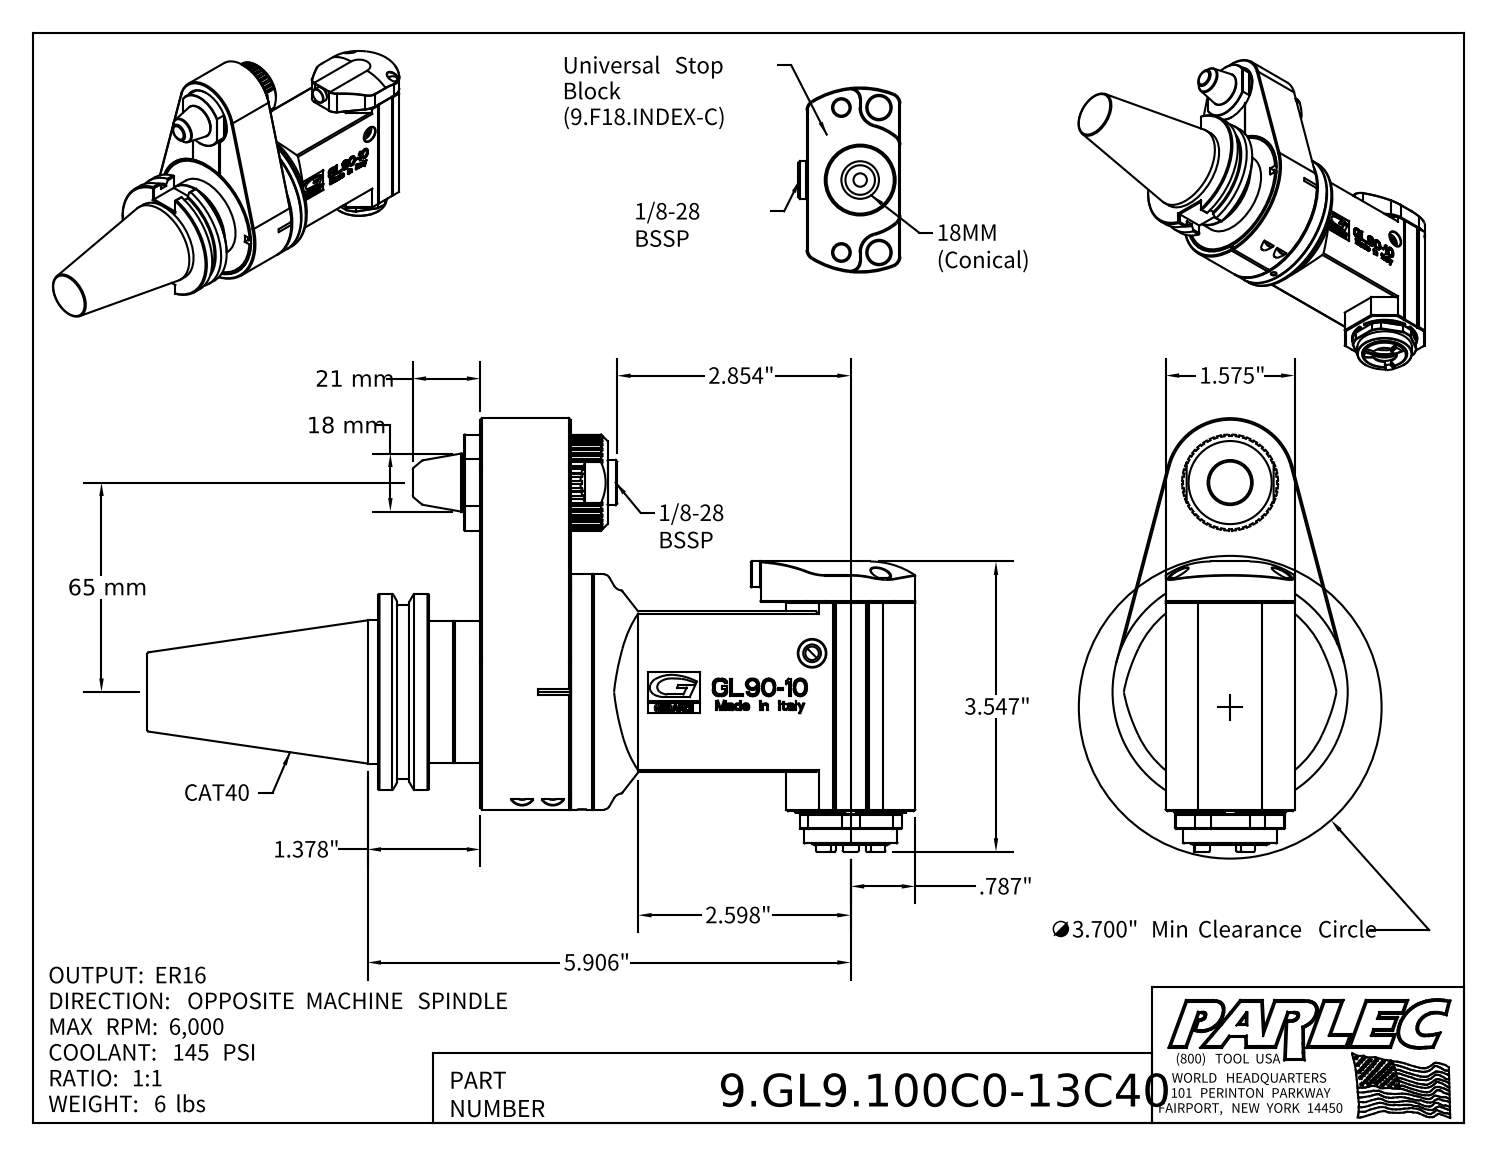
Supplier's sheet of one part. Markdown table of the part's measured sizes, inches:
| quantity | value |
| --- | --- |
| part name | 9.GL9.100C0-13C40; 9_GL9_100C0; 9_GAO_446_C (Classic, Type 0, Cat40, 65mm) |
| STEP written by | Autodesk Inventor 2022 (AUTOMOTIVE_DESIGN) |
| units | inches |
| bodies | 3 solids, 2146 faces (1648 planar, 194 cylindrical, 304 other) |
| overall size | 9.386 × 5.299 × 2.874 |
| volume | 32.45 in³ |
| surface area | 185.1 in² |
| round holes (diameter × count) | 0.236 × 5, 0.165 × 4, 0.335 × 2, 0.512 × 2, 1.26 × 2, 1.378 × 2, 0.098 × 1, 0.217 × 1, 0.362 × 1, 0.681 × 1, 0.709 × 1, 0.886 × 1 |
| round bosses / shafts (diameter × count) | 0.551 × 2, 0.217 × 2, 0.197 × 2, 2.874 × 1, 2.559 × 1, 2.498 × 1, 2.215 × 1, 2.165 × 1 |
| partial cylindrical surfaces (radius × count) | 0.394 × 4, 0.079 × 3, 0.984 × 3, 1.106 × 3, 0.074 × 2, 0.097 × 2, 0.108 × 2, 0.133 × 2 |
| main face-to-face distances | 1.102, 1.575, 0.28, 0.823, 0.626, 1.004, 1.969, 0.827, 0.098, 0.181 |
| hole center spacings | 0.555, 0.68, 1.383, 1.946, 0.374, 0.512, 0.63, 0.728 |
